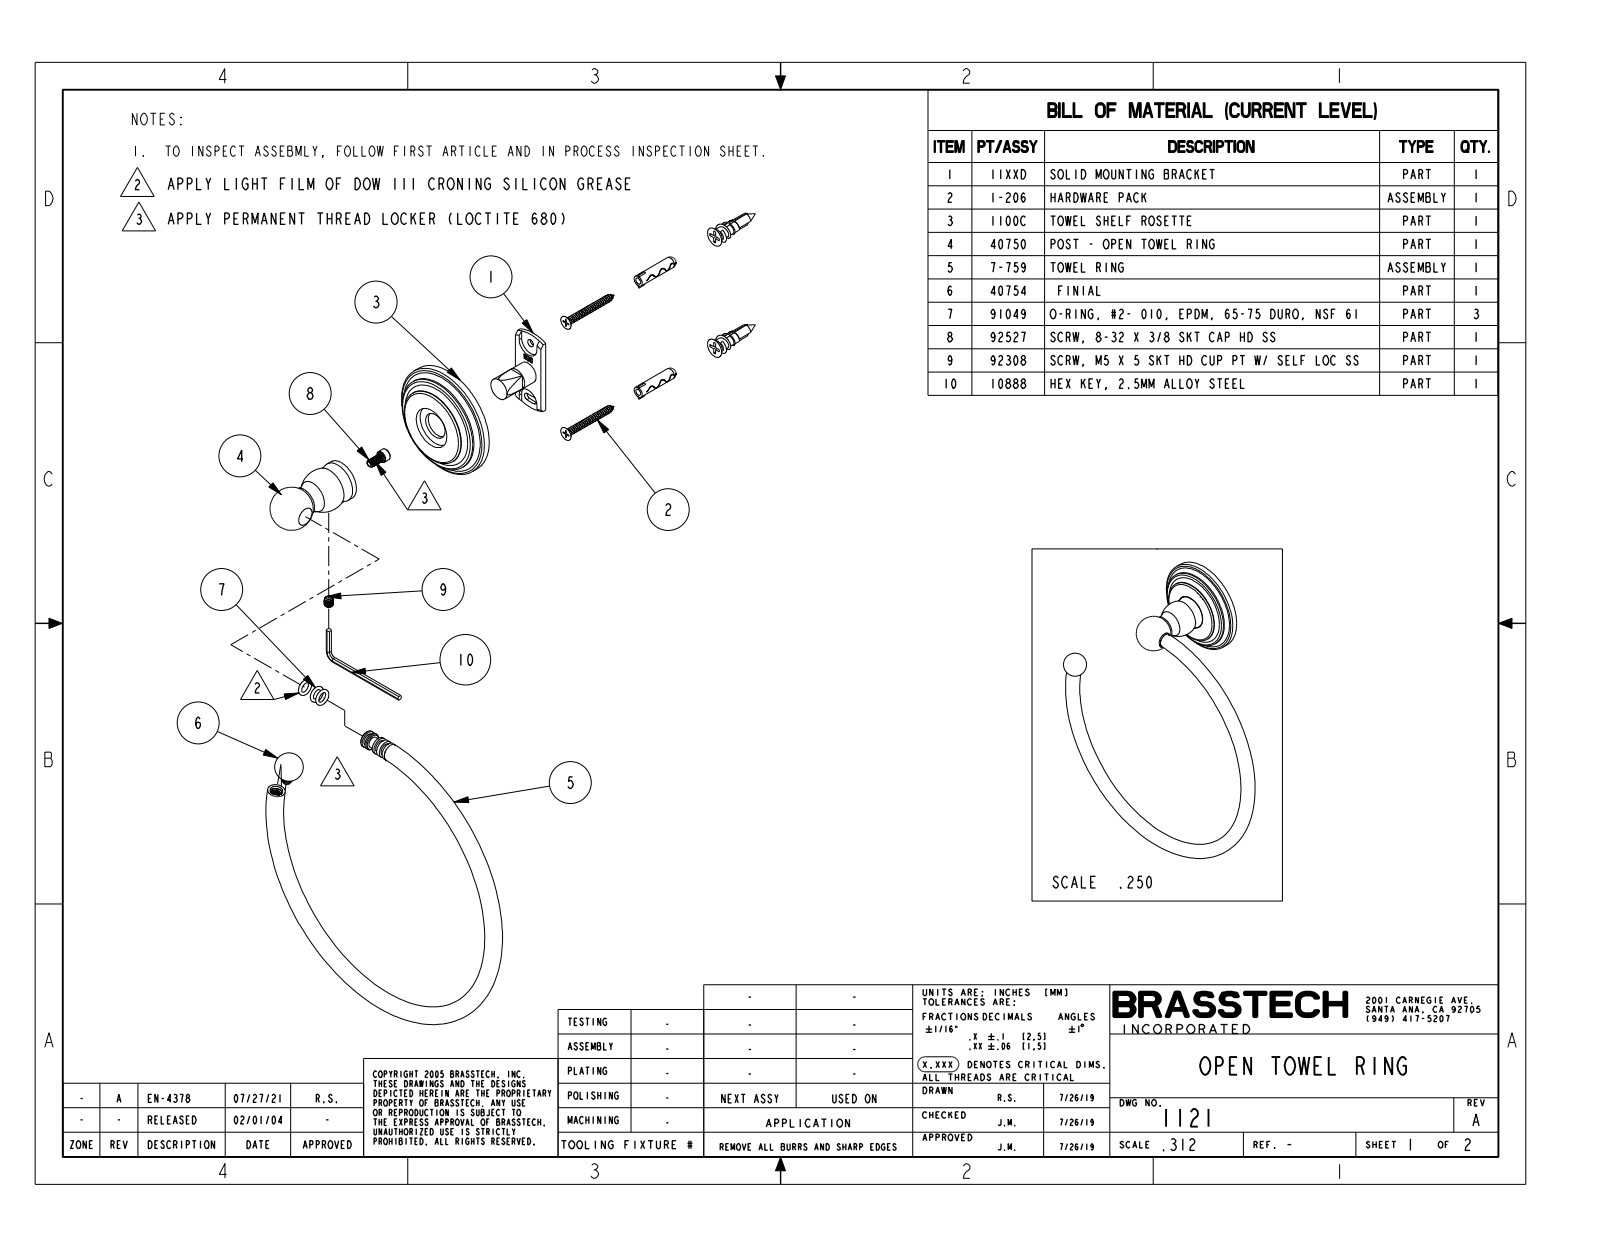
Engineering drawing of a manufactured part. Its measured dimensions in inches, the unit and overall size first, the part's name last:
Units: inches
Overall size (bounding box): 8.279 × 7.227 × 2.422
Round holes (diameter × count): ⌀0.413 ×1
Round bosses / shafts (diameter × count): ⌀2.56 ×1, ⌀2.182 ×1, ⌀1.748 ×1, ⌀0.39 ×1
Main face-to-face distances: 0.512, 0.362, 0.15, 0.189, 0.173, 0.323, 0.465
Volume: 5.108 in³ · Surface area: 39.96 in²
Bodies: 1 solid, 42 faces (8 planar, 10 cylindrical, 24 other)
Part name (STEP PRODUCT): 1121
STEP written by: CREO PARAMETRIC BY PTC INC, 2018400 (AUTOMOTIVE_DESIGN)
